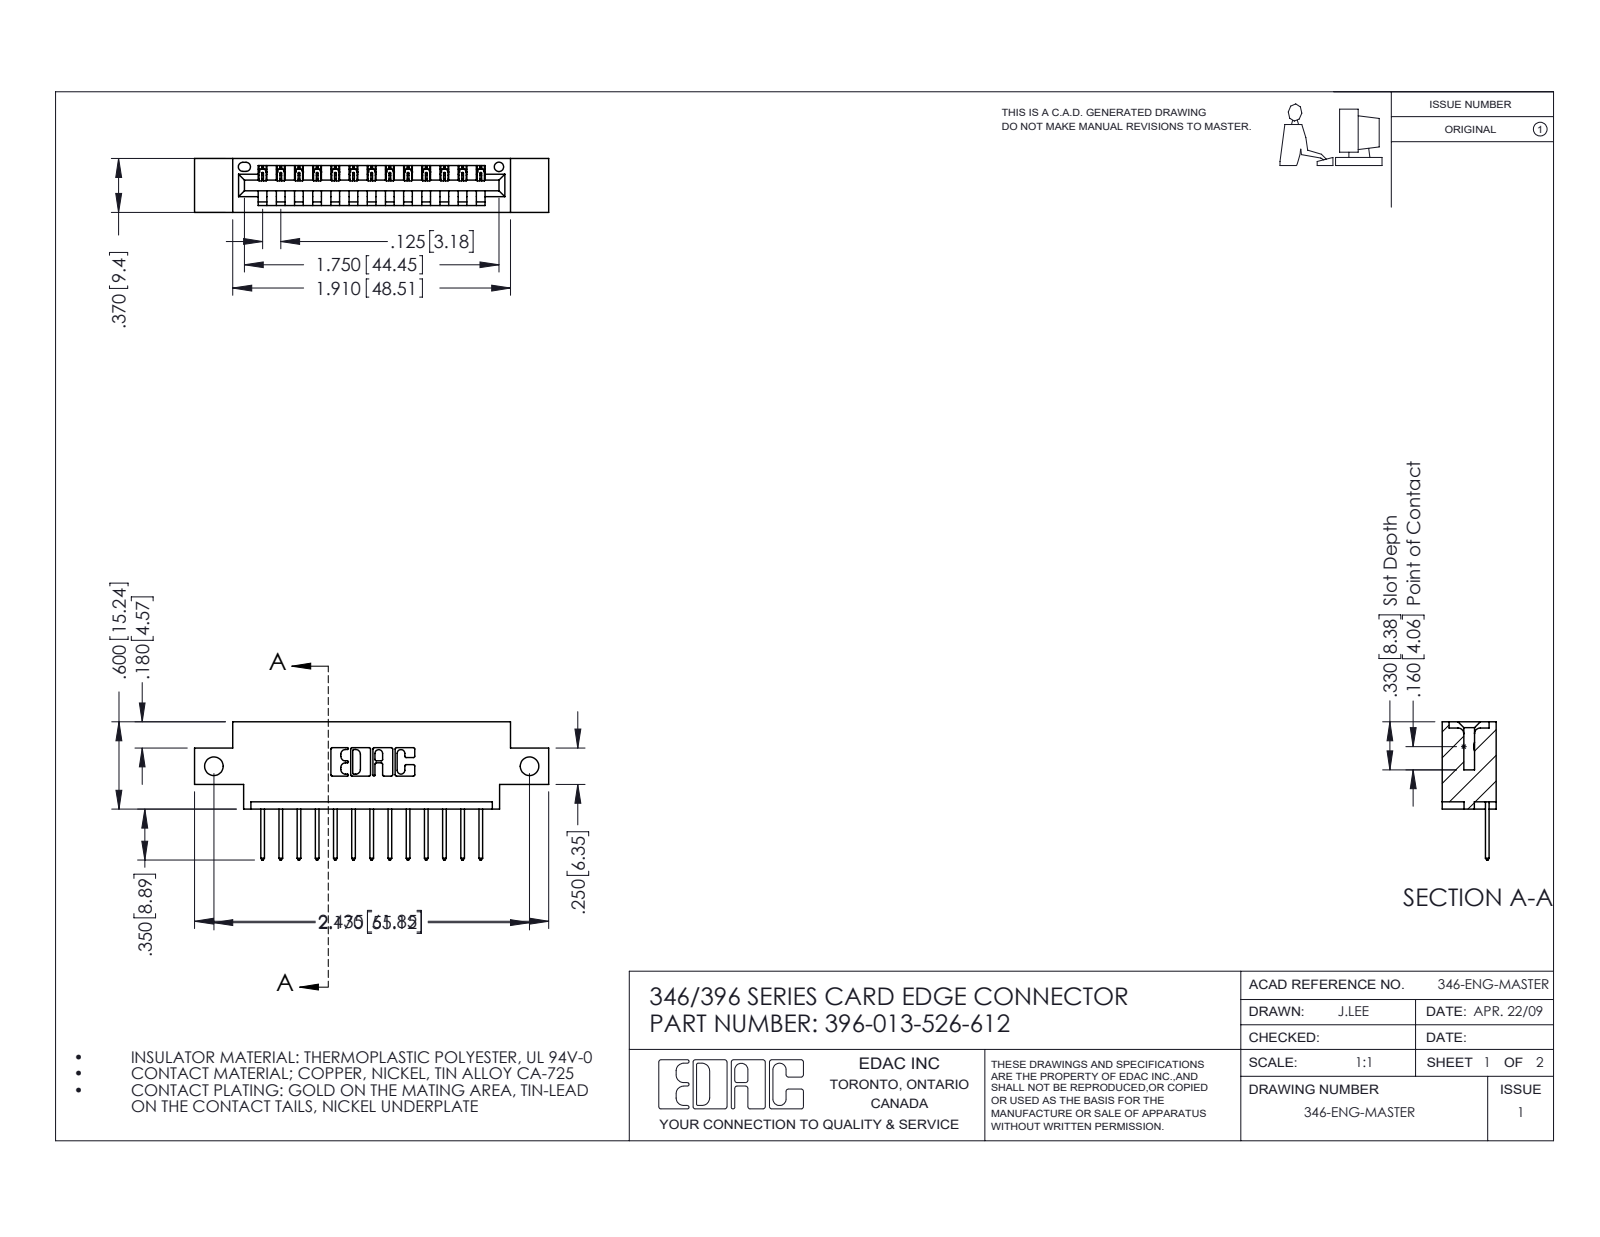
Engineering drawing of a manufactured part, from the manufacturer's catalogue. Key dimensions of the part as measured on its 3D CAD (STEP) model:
Part name (STEP PRODUCT): 396-013-526-612; 345-292-001_345-293-126; 346 Part_0.170 Offset - Side Mount
STEP written by: SolidWorks 2016 (CONFIG_CONTROL_DESIGN)
Units: inches
Bodies: 14 solids, 880 faces (600 planar, 280 cylindrical, 0 other)
Overall size (bounding box): 2.435 × 0.95 × 0.37
Volume: 0.334 in³ · Surface area: 10.11 in²
Round holes (diameter × count): ⌀0.128 ×2, ⌀0.064 ×1
Partial cylindrical surfaces — rounded edges, fillets, slot ends (radius × count): R0.006 ×26, R0.01 ×26, R0.01 ×22, R0.007 ×6, R0.031 ×6, R0.026 ×3, R0.031 ×2, R0.04 ×2
Main face-to-face distances: 0.25, 0.37, 0.048, 0.322, 0.072, 0.298, 0.025, 0.148, 0.222, 0.1
Hole centre spacings: 2.17
